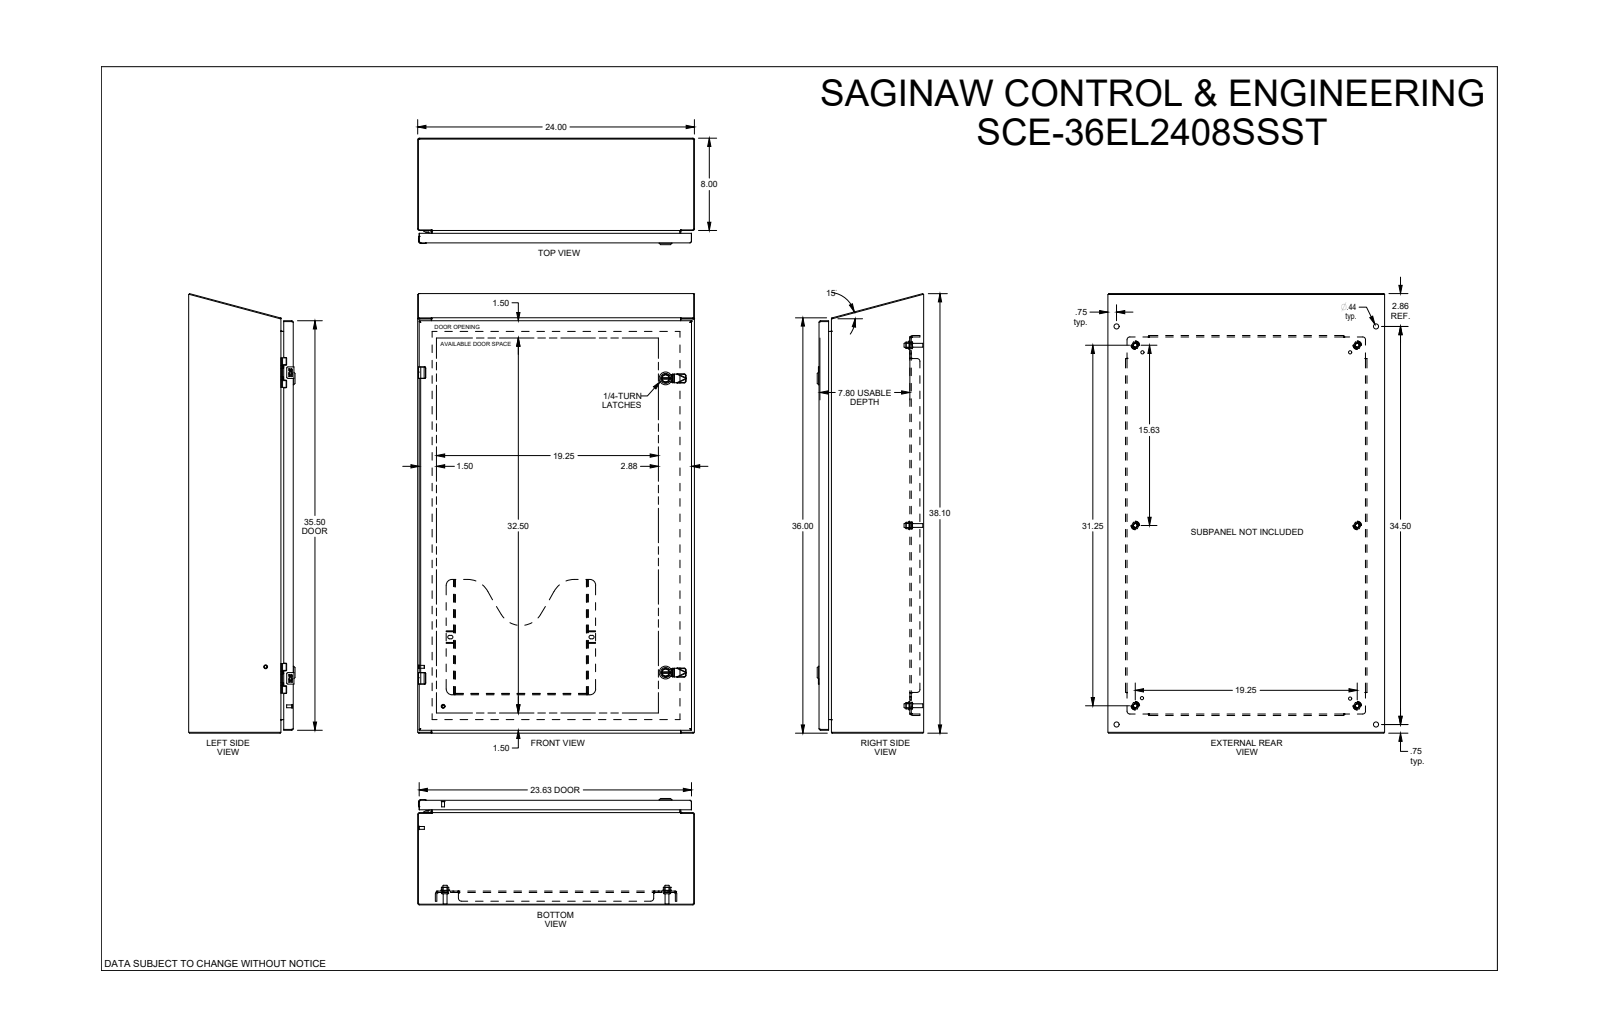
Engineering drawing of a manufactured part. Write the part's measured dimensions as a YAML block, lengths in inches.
part_name: "SCE-36EL2408SSST"
step_written_by: "SolidWorks 2019 (CONFIG_CONTROL_DESIGN)"
units: inches
bodies: {solids: 0, faces: 2954, planar: 1335, cylindrical: 779, other: 840}
overall_size: [38.106, 24, 9.23]
round_holes:
  - {diameter: 0.367, count: 6}
  - {diameter: 0.5, count: 6}
  - {diameter: 0.172, count: 4}
  - {diameter: 0.205, count: 4}
  - {diameter: 0.244, count: 4}
  - {diameter: 0.266, count: 4}
  - {diameter: 0.281, count: 4}
  - {diameter: 0.375, count: 4}
  - {diameter: 0.437, count: 4}
  - {diameter: 0.156, count: 2}
  - {diameter: 0.197, count: 2}
  - {diameter: 0.218, count: 2}
round_bosses_or_shafts:
  - {diameter: 0.366, count: 6}
  - {diameter: 0.332, count: 6}
  - {diameter: 0.17, count: 6}
  - {diameter: 0.25, count: 4}
  - {diameter: 0.248, count: 4}
  - {diameter: 0.196, count: 3}
  - {diameter: 1.102, count: 2}
  - {diameter: 0.866, count: 2}
partial_cylinders:
  - {radius: 0.012, count: 56}
  - {radius: 0.01, count: 40}
  - {radius: 0.015, count: 32}
  - {radius: 0.04, count: 23}
  - {radius: 0.02, count: 20}
  - {radius: 0.029, count: 12}
  - {radius: 0.06, count: 11}
  - {radius: 0.07, count: 10}
face_to_face_distances: [0.075, 0.075, 8.923, 8.998, 9.073, 8.998, 1.2, 7.873, 1, 0.125]
hole_center_spacings: [26.5, 0.985, 0.02, 0.875, 2.298, 4.493, 15.625, 17.326]
